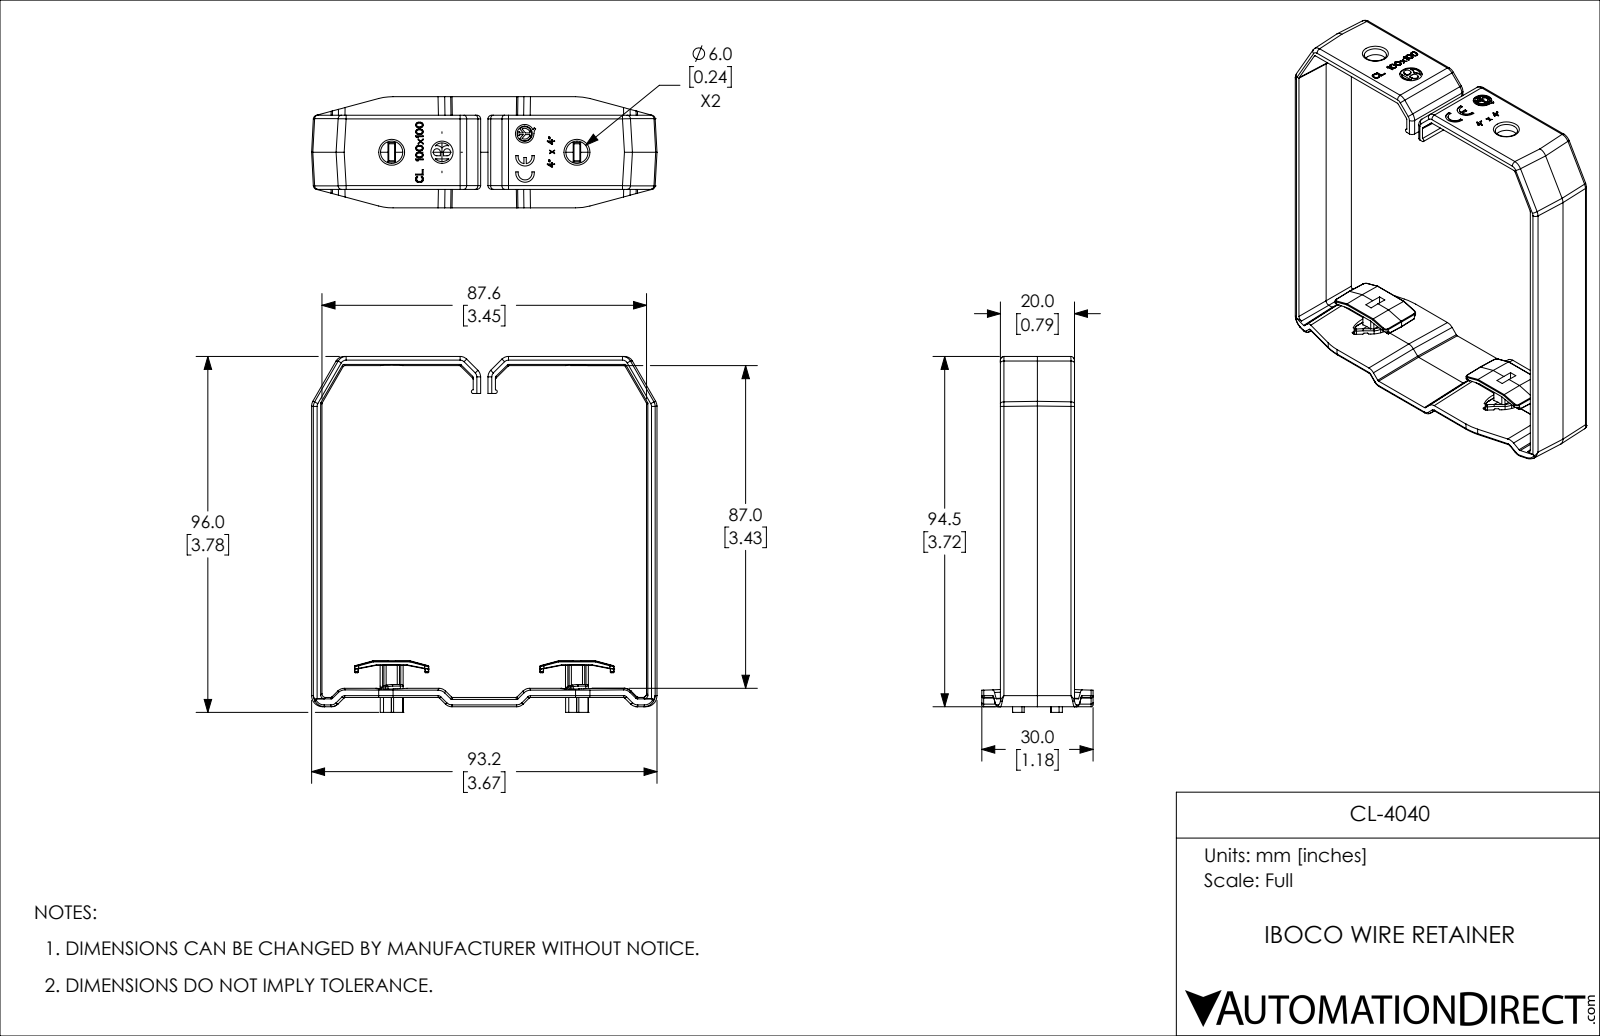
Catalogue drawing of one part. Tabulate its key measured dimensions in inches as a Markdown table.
| quantity | value |
| --- | --- |
| part name | CL-4040 |
| STEP written by | SolidWorks 2019 (CONFIG_CONTROL_DESIGN) |
| units | inches |
| bodies | 1 solid, 965 faces (608 planar, 280 cylindrical, 77 other) |
| overall size | 3.78 × 3.669 × 1.181 |
| volume | 1.149 in³ |
| surface area | 29.85 in² |
| round holes (diameter × count) | 0.236 × 3, 0.197 × 1 |
| round bosses / shafts (diameter × count) | 0.161 × 1 |
| partial cylindrical surfaces (radius × count) | 0.02 × 66, 0.008 × 36, 0.039 × 34, 0.098 × 30, 0.012 × 12, 0.016 × 12, 0.026 × 4, 0.047 × 4 |
| main face-to-face distances | 3.446, 3.665, 3.422, 0.098, 3.622, 3.72, 3.52, 0.787, 1.392, 0.079 |
| hole center spacings | 0.535, 0.589, 0.9, 1.427, 1.434, 1.969 |
